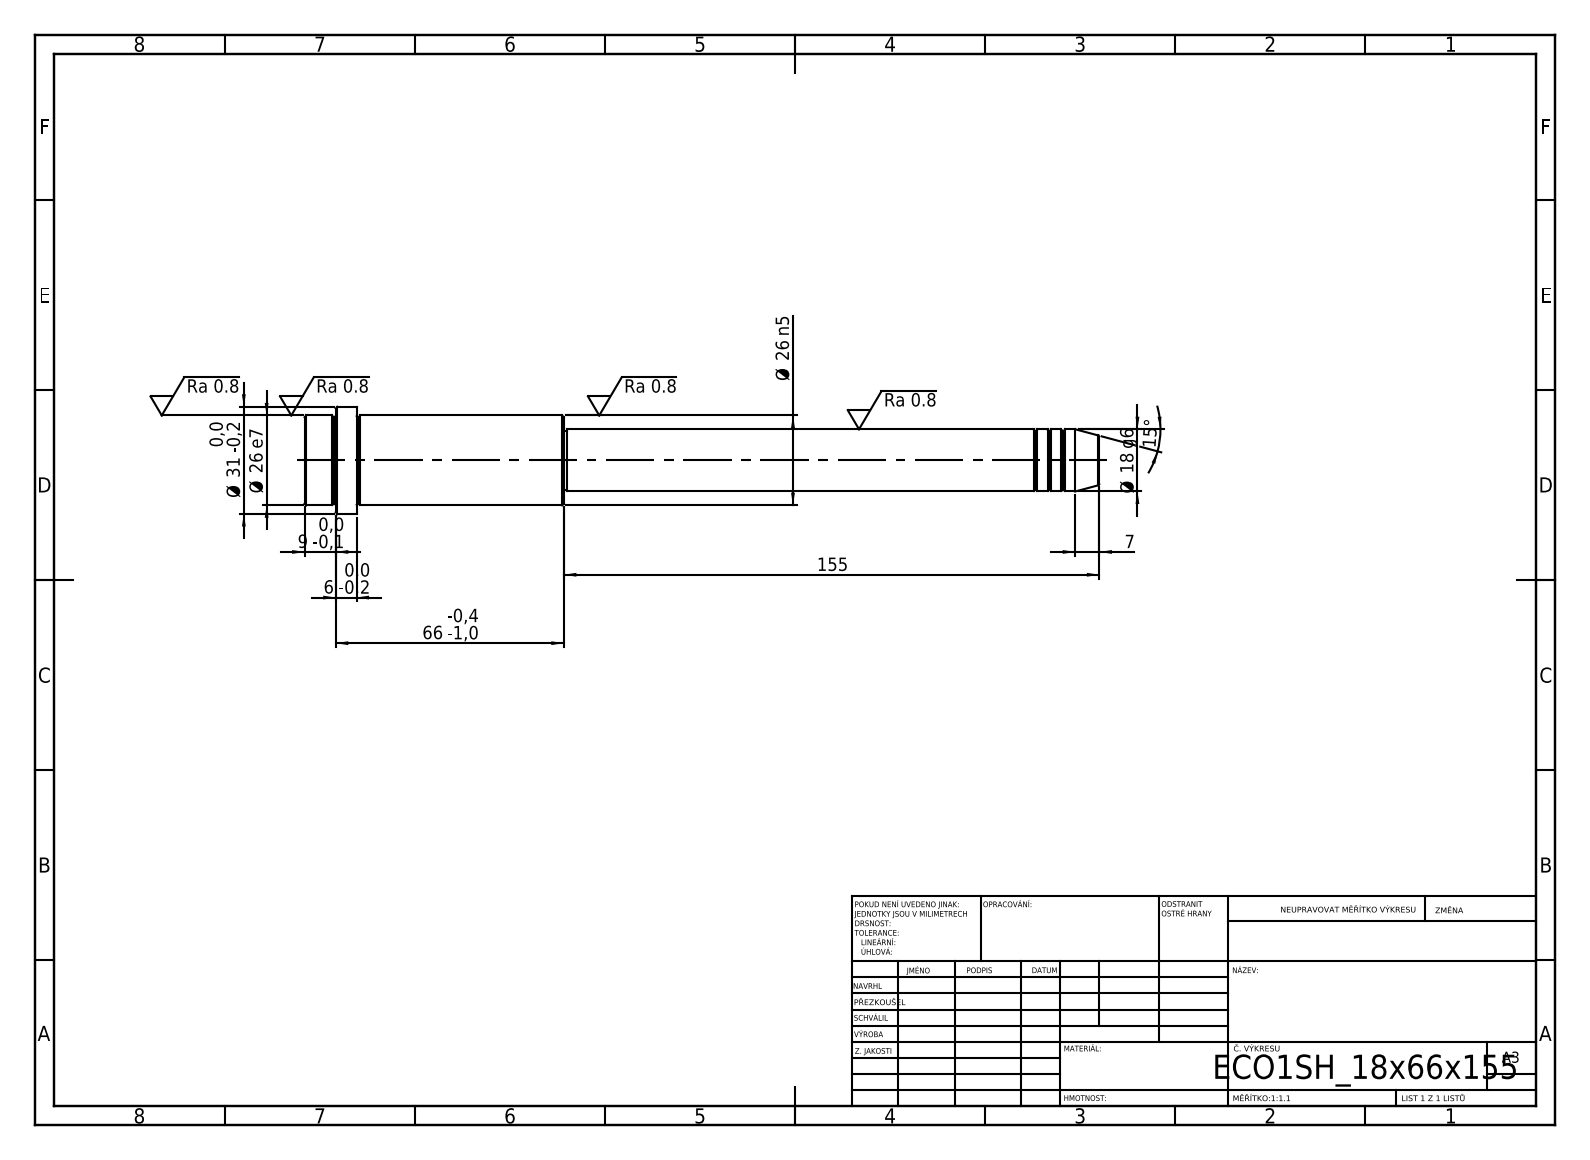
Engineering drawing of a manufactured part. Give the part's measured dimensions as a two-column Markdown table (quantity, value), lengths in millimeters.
| quantity | value |
| --- | --- |
| STEP written by | SolidWorks 2019 (CONFIG_CONTROL_DESIGN) |
| units | millimeters |
| bodies | 1 solid, 52 faces (6 planar, 16 cylindrical, 30 other) |
| overall size | 230 × 31 × 31 |
| volume | 80 071 mm³ |
| surface area | 16 515 mm² |
| round bosses / shafts (diameter × count) | 31 × 1, 26 × 1, 18 × 1, 17 × 1 |
| main face-to-face distances | 75, 60, 15, 66, 6, 9, 155, 215, 221, 230 |
